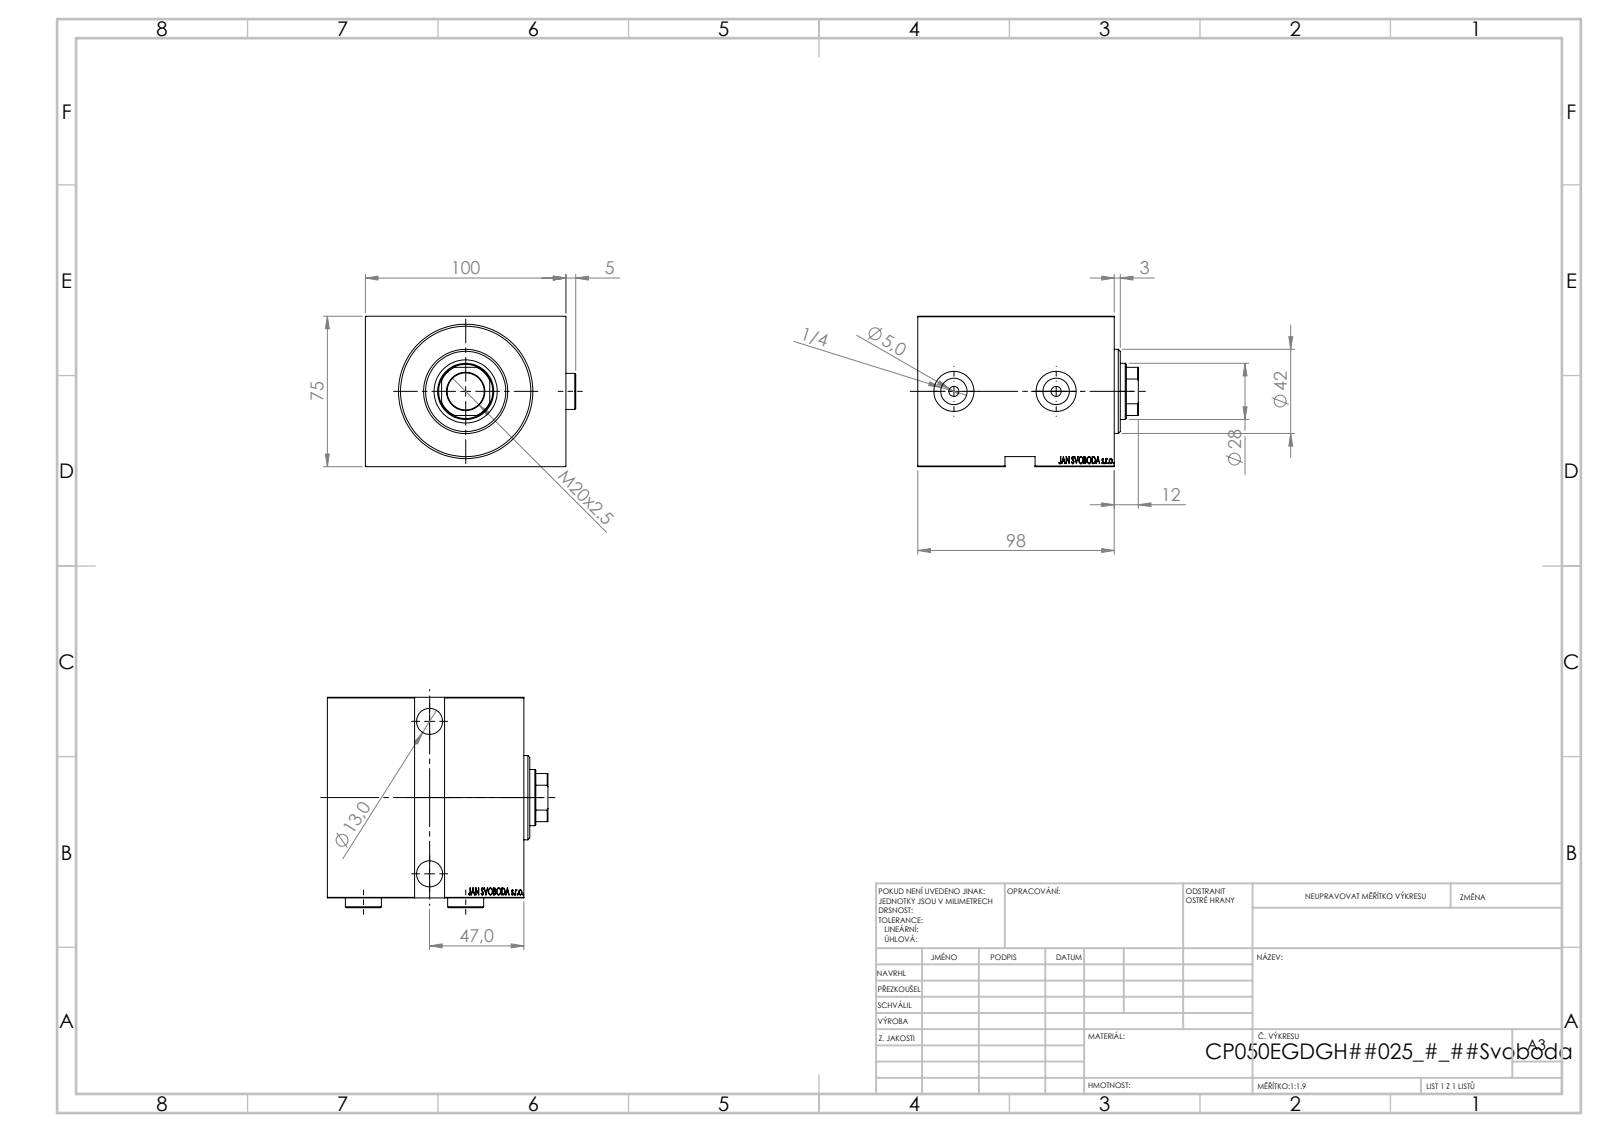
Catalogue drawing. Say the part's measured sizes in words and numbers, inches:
The part is named "V450CM_VC_B; V450CM_E_VCP; Zatka_OIL_PORT; V450CM_E_Body". Its 3-D file was written by "SolidWorks 2019 (CONFIG_CONTROL_DESIGN)". It is 5 solids with 902 faces: 444 planar, 60 cylindrical and 398 other. Overall it measures 4.331 by 4.13 by 2.953 inches. Its volume is 41.04 cubic inches and its surface area 157.1 square inches. Round holes: 2 of diameter 0.197, 2 of diameter 0.512, 2 of diameter 0.518, 2 of diameter 0.748, 2 of diameter 0.787, 1 of diameter 0.728, 1 of diameter 1.102, 1 of diameter 1.24, 1 of diameter 1.969, 1 of diameter 2.559. Round bosses or shafts: 2 of diameter 0.709, 1 of diameter 2.047, 1 of diameter 1.654. Partial cylindrical surfaces (rounded edges, fillets, slot ends): 1 of radius 0.531. The main face-to-face distances are 2.953, 3.937, 3.858, 0.197, 0.551, 3.307, 3.11, 3.661, 3.205, 2.654. The hole center spacings are 2.008, 2.992.
